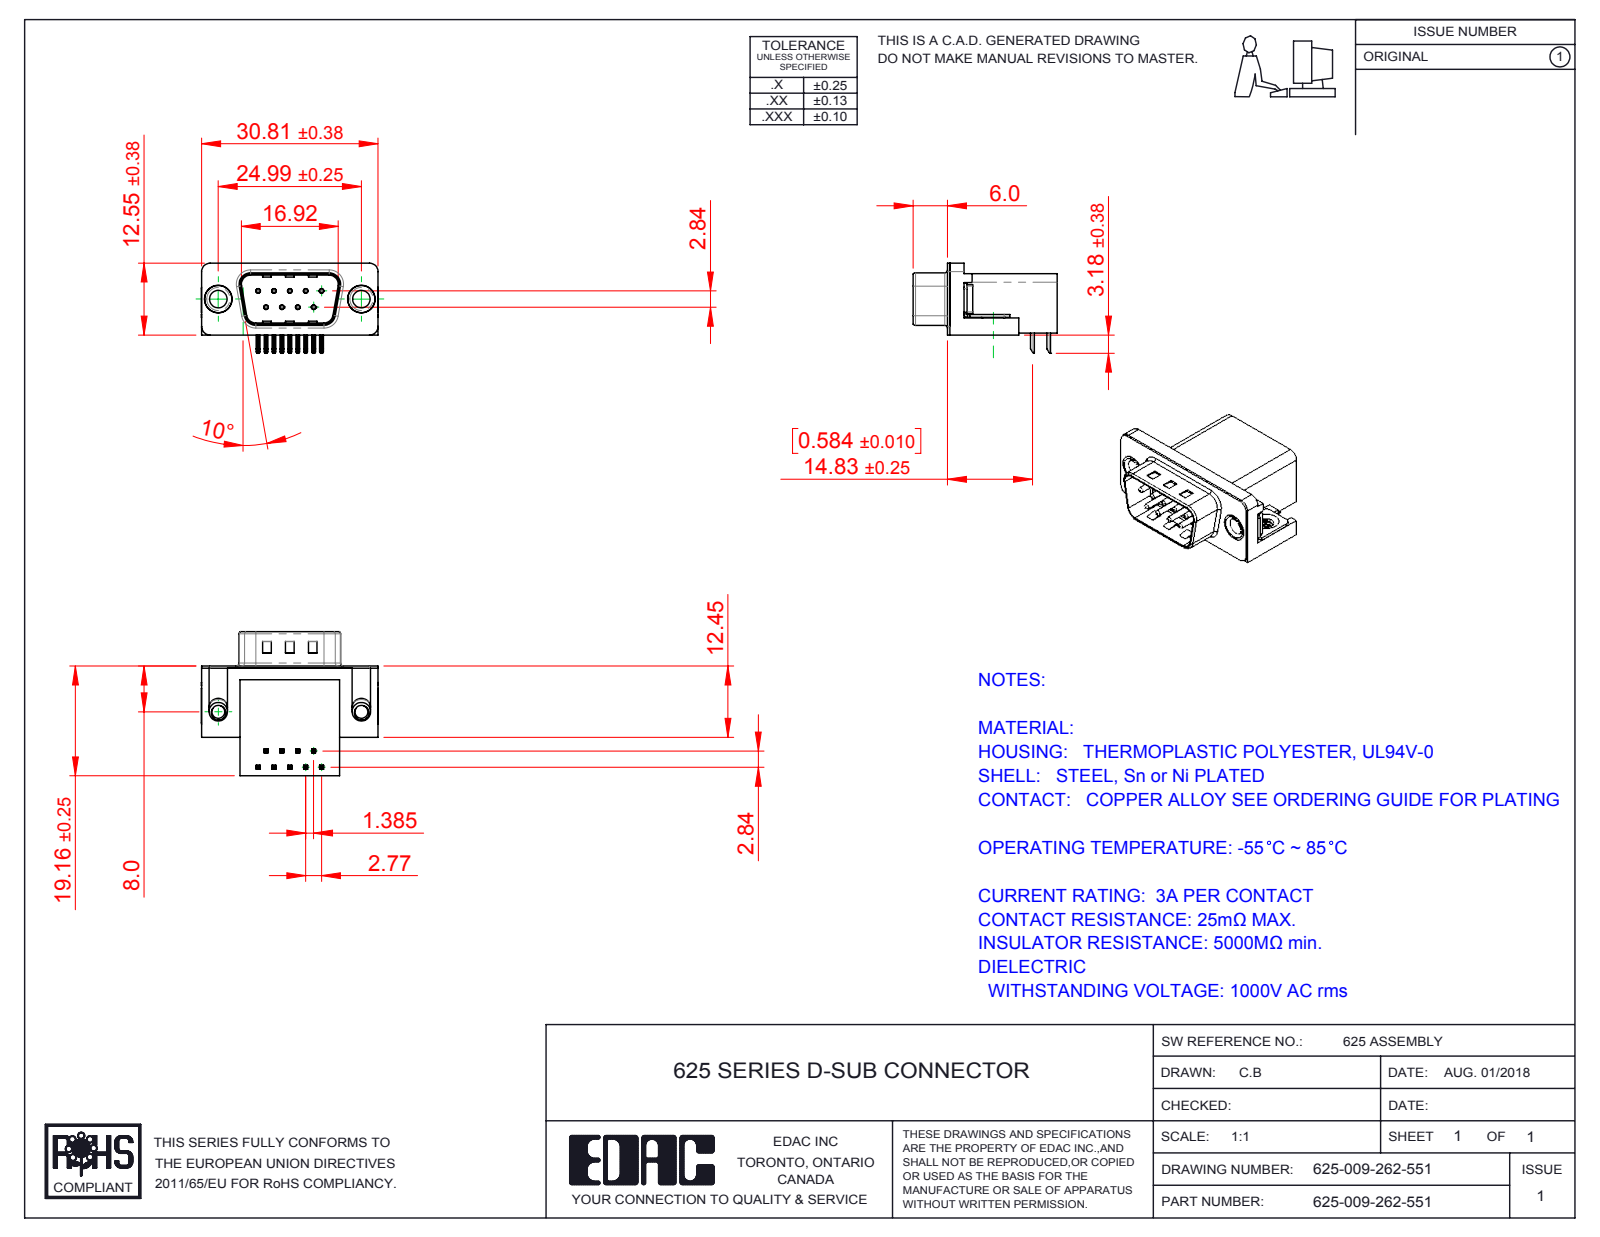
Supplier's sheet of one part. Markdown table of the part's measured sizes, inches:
| quantity | value |
| --- | --- |
| part name | 625 Shell_9 Socket; 625 Contact Top; 625-009-262-551; 625 Thru Hole Rivet (+3 more) |
| STEP written by | SolidWorks 2016 (CONFIG_CONTROL_DESIGN) |
| units | inches |
| bodies | 15 solids, 985 faces (575 planar, 311 cylindrical, 99 other) |
| overall size | 1.216 × 0.991 × 0.619 |
| volume | 0.273 in³ |
| surface area | 7.761 in² |
| round holes (diameter × count) | 0.014 × 9, 0.031 × 9, 0.089 × 2, 0.12 × 2, 0.157 × 2, 0.189 × 2, 0.197 × 2 |
| round bosses / shafts (diameter × count) | 0.03 × 9, 0.193 × 2, 0.187 × 2, 0.152 × 2, 0.128 × 2 |
| partial cylindrical surfaces (radius × count) | 0.01 × 44, 0.005 × 18, 0.039 × 16, 0.02 × 9, 0.059 × 8, 0.063 × 8, 0.035 × 4, 0.079 × 4 |
| main face-to-face distances | 0.016, 0.407, 0.739, 0.754, 0.114, 0.64, 0.098, 0.014, 0.421, 0.264 |
| hole center spacings | 0.124, 0.109, 0.218, 0.198, 0.198, 0.327, 0.294, 0.295 |
